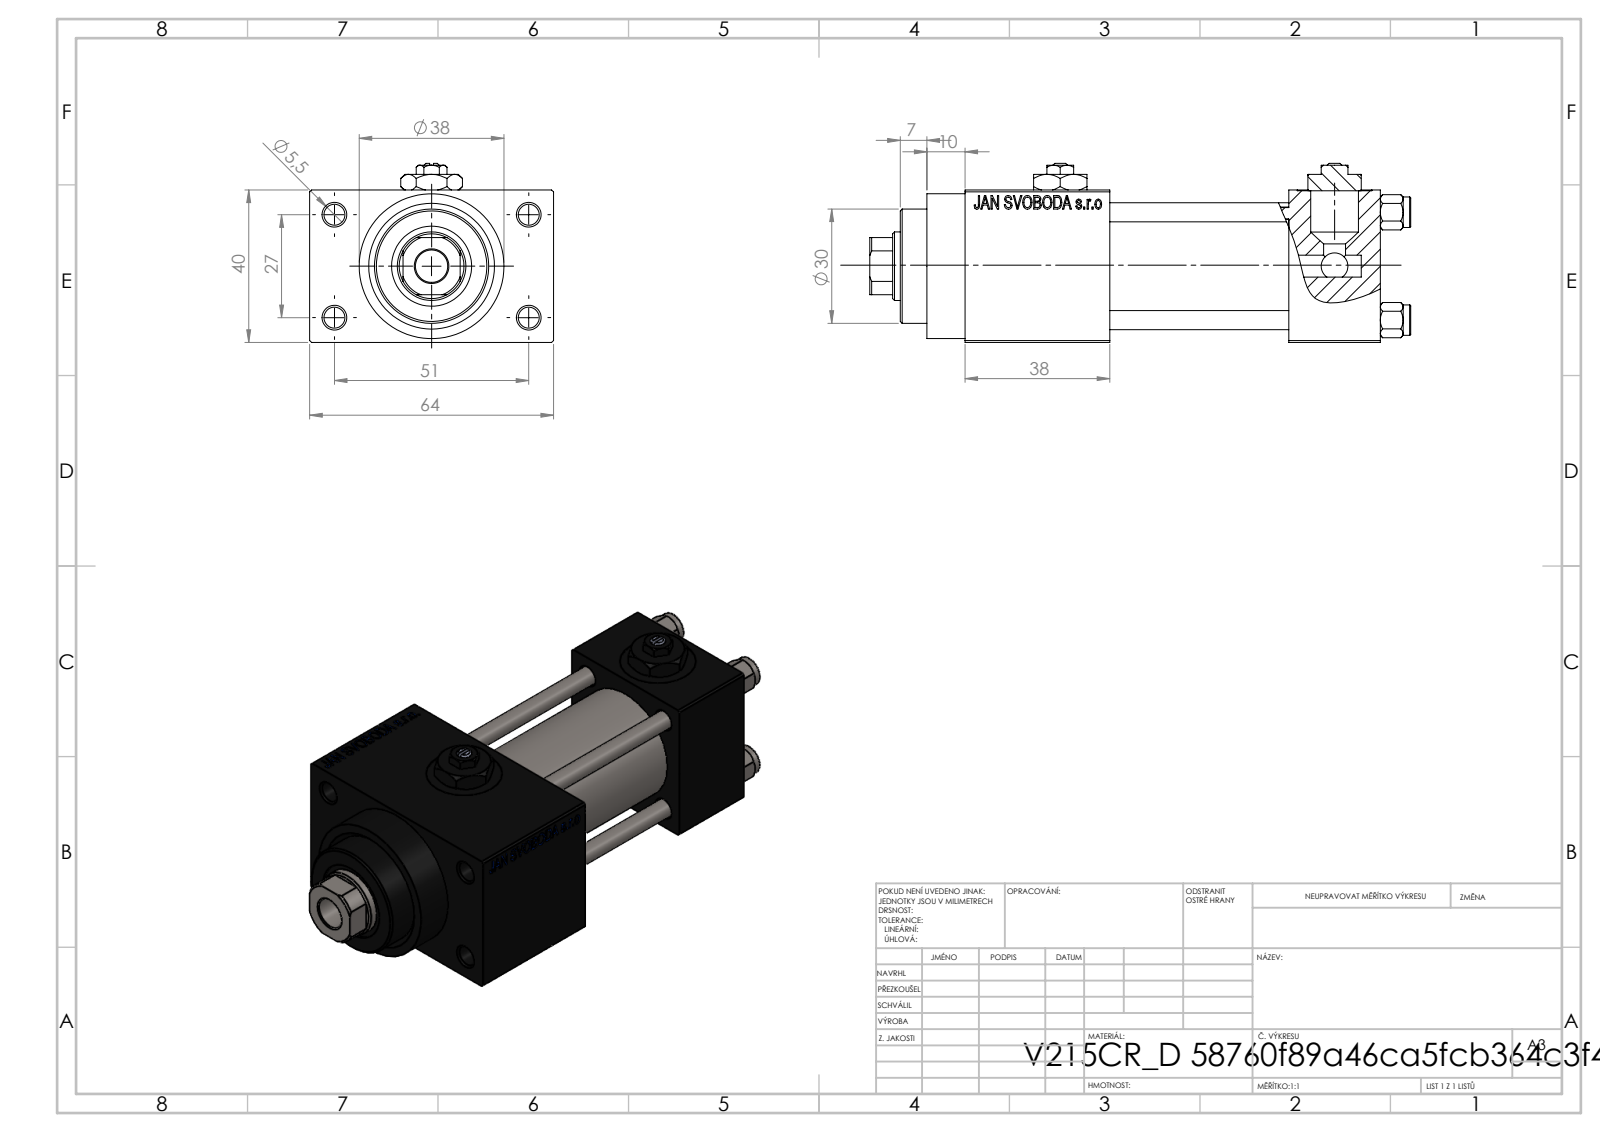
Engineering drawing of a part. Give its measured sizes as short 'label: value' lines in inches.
name: Zatka_pro_OIL_PORT; V215CR_VCP_D; V215_VC_A; V215CR_D_Body (+2 more)
written by: SolidWorks 2019 (CONFIG_CONTROL_DESIGN)
unit: in
bodies: 13 solids, 1200 faces (541 planar, 97 cylindrical, 562 other)
size: 5.591 × 2.52 × 1.85
volume: 10.87 in³; area: 102.7 in²
holes: 5× ⌀0.787, 4× ⌀0.197, 4× ⌀0.217, 4× ⌀0.518, 3× ⌀0.276, 1× ⌀0.335, 1× ⌀0.709, 1× ⌀0.827, 1× ⌀0.984, 1× ⌀1.181
bosses: 4× ⌀0.315, 1× ⌀1.496, 1× ⌀1.22
rounds: 1× R0.335
face distances: 1.575, 0.472, 1.85, 2.047, 0.945, 2.795, 1.496, 3.346, 4.291, 2.52
hole spacings: 0.448, 0.788, 1.114, 1.136, 1.177, 1.561, 1.903, 1.063
